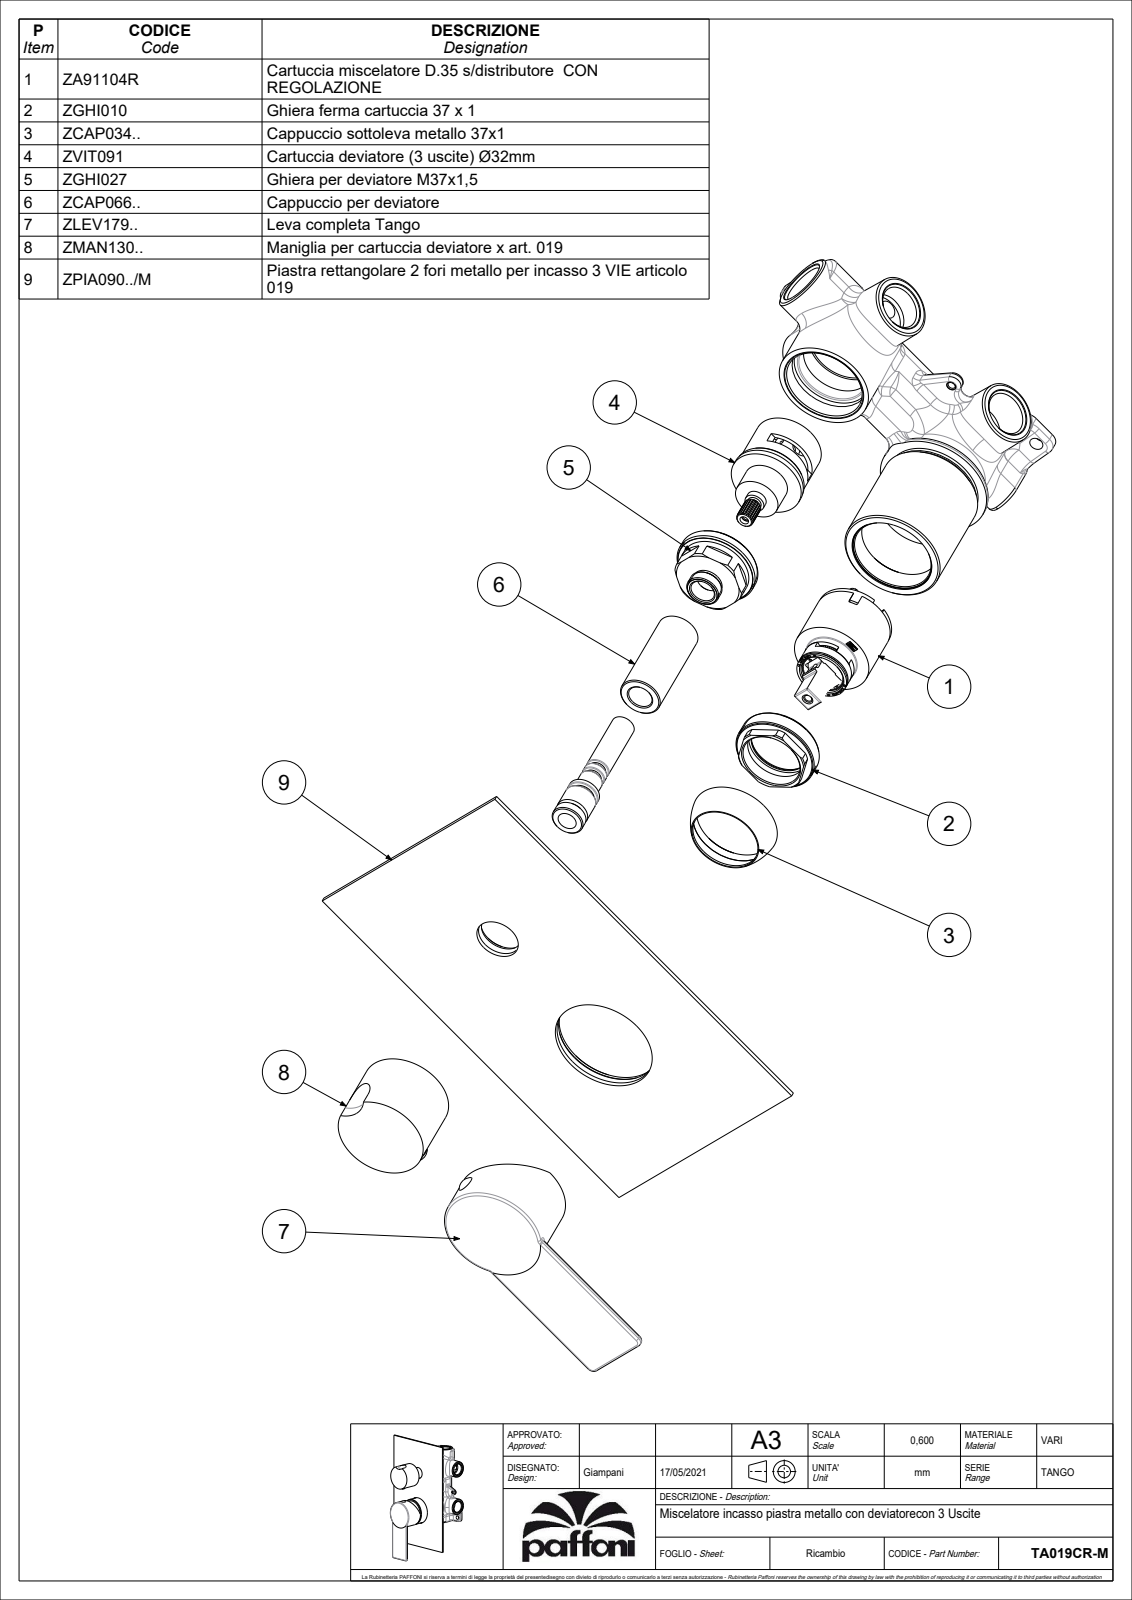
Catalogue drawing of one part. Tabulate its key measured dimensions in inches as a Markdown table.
| quantity | value |
| --- | --- |
| part name | TA018CR-M |
| STEP written by | CREO PARAMETRIC BY PTC INC, 2020044 (CONFIG_CONTROL_DESIGN) |
| units | inches |
| bodies | 2 solids, 227 faces (73 planar, 86 cylindrical, 68 other) |
| overall size | 8.071 × 4.724 × 2.372 |
| volume | 6.646 in³ |
| surface area | 133.8 in² |
| round holes (diameter × count) | 0.118 × 2, 0.165 × 2, 1.417 × 2, 0.126 × 1, 0.433 × 1, 0.583 × 1, 1.205 × 1, 1.476 × 1 |
| round bosses / shafts (diameter × count) | 0.299 × 2, 0.217 × 2, 1.791 × 1, 1.764 × 1, 1.575 × 1, 0.945 × 1, 0.736 × 1 |
| partial cylindrical surfaces (radius × count) | 0.039 × 6, 0.059 × 4, 0.02 × 2, 0.118 × 2, 0.138 × 1, 0.492 × 1 |
| main face-to-face distances | 0.079, 2.11, 2.307, 2.228, 0.118, 2.189, 1.098, 0.138, 0.02, 1.177 |
| hole center spacings | 0.071, 0.394, 2.677, 3.071 |
